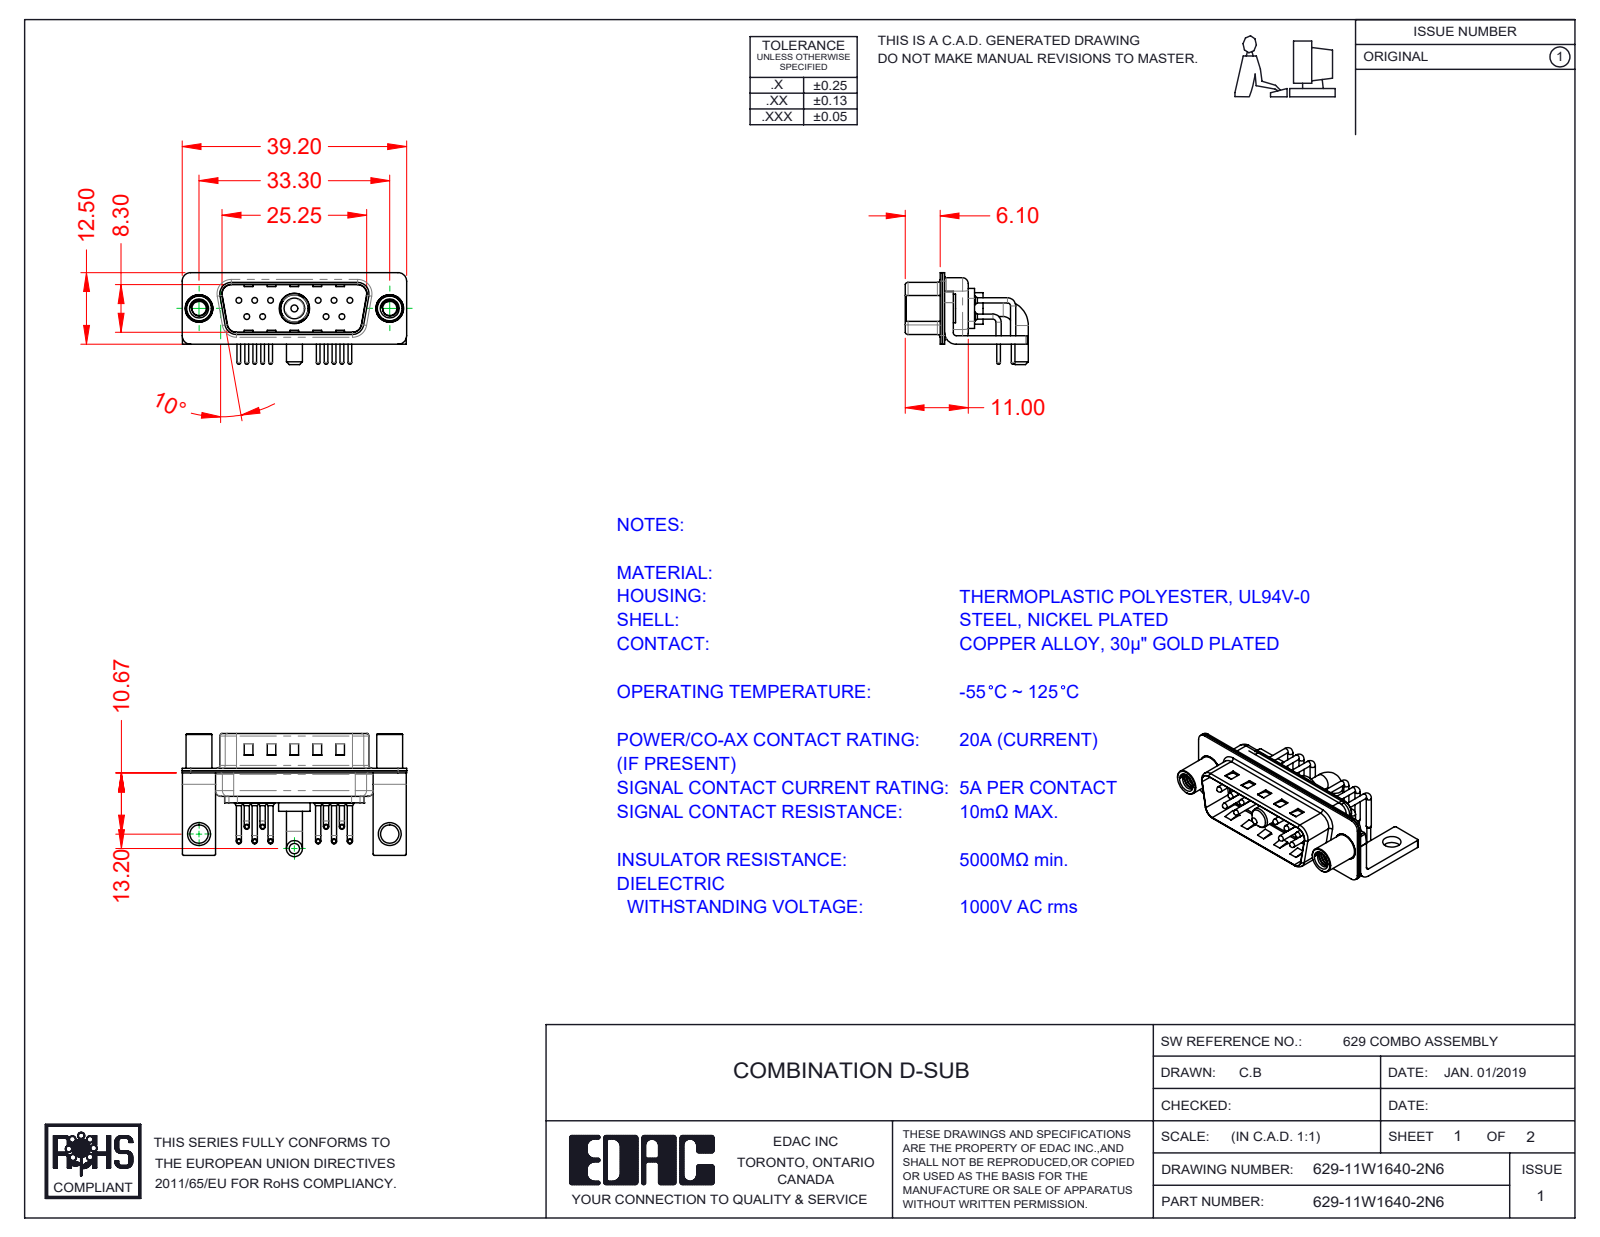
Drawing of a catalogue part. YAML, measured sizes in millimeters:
part_name: "629Combo Shell Front_15 Contacts; 629Combo Housing_11W1; 629Combo Contact Row 1; 629Combo Threaded Standoff_D (+5 more)"
step_written_by: "SolidWorks 2020 (CONFIG_CONTROL_DESIGN)"
units: millimeters
bodies: {solids: 19, faces: 1594, planar: 820, cylindrical: 590, other: 184}
overall_size: [39.2, 21.5, 16.05]
volume: 2447
surface_area: 6158
round_holes:
  - {diameter: 0.75, count: 10}
  - {diameter: 1.6, count: 10}
  - {diameter: 2, count: 10}
  - {diameter: 2.5, count: 2}
  - {diameter: 3.2, count: 2}
  - {diameter: 4, count: 2}
  - {diameter: 4.8, count: 2}
  - {diameter: 4.85, count: 1}
  - {diameter: 5.3, count: 1}
round_bosses_or_shafts:
  - {diameter: 0.9, count: 20}
  - {diameter: 1.5, count: 10}
  - {diameter: 1, count: 10}
  - {diameter: 0.65, count: 10}
  - {diameter: 5, count: 2}
  - {diameter: 4.9, count: 2}
  - {diameter: 4.5, count: 2}
  - {diameter: 2.8, count: 2}
partial_cylinders:
  - {radius: 0.25, count: 16}
  - {radius: 1.5, count: 16}
  - {radius: 2, count: 13}
  - {radius: 1.01, count: 10}
  - {radius: 0.5, count: 9}
  - {radius: 1.6, count: 8}
  - {radius: 1, count: 7}
  - {radius: 0.6, count: 4}
face_to_face_distances: [0.4, 0.8, 1.5, 9.5, 9.1, 8.7, 9.9, 0.6, 1.9, 5.2]
hole_center_spacings: [3.16, 2.77, 13.85, 11.08, 16.62, 5.03, 5.04, 5.54]
